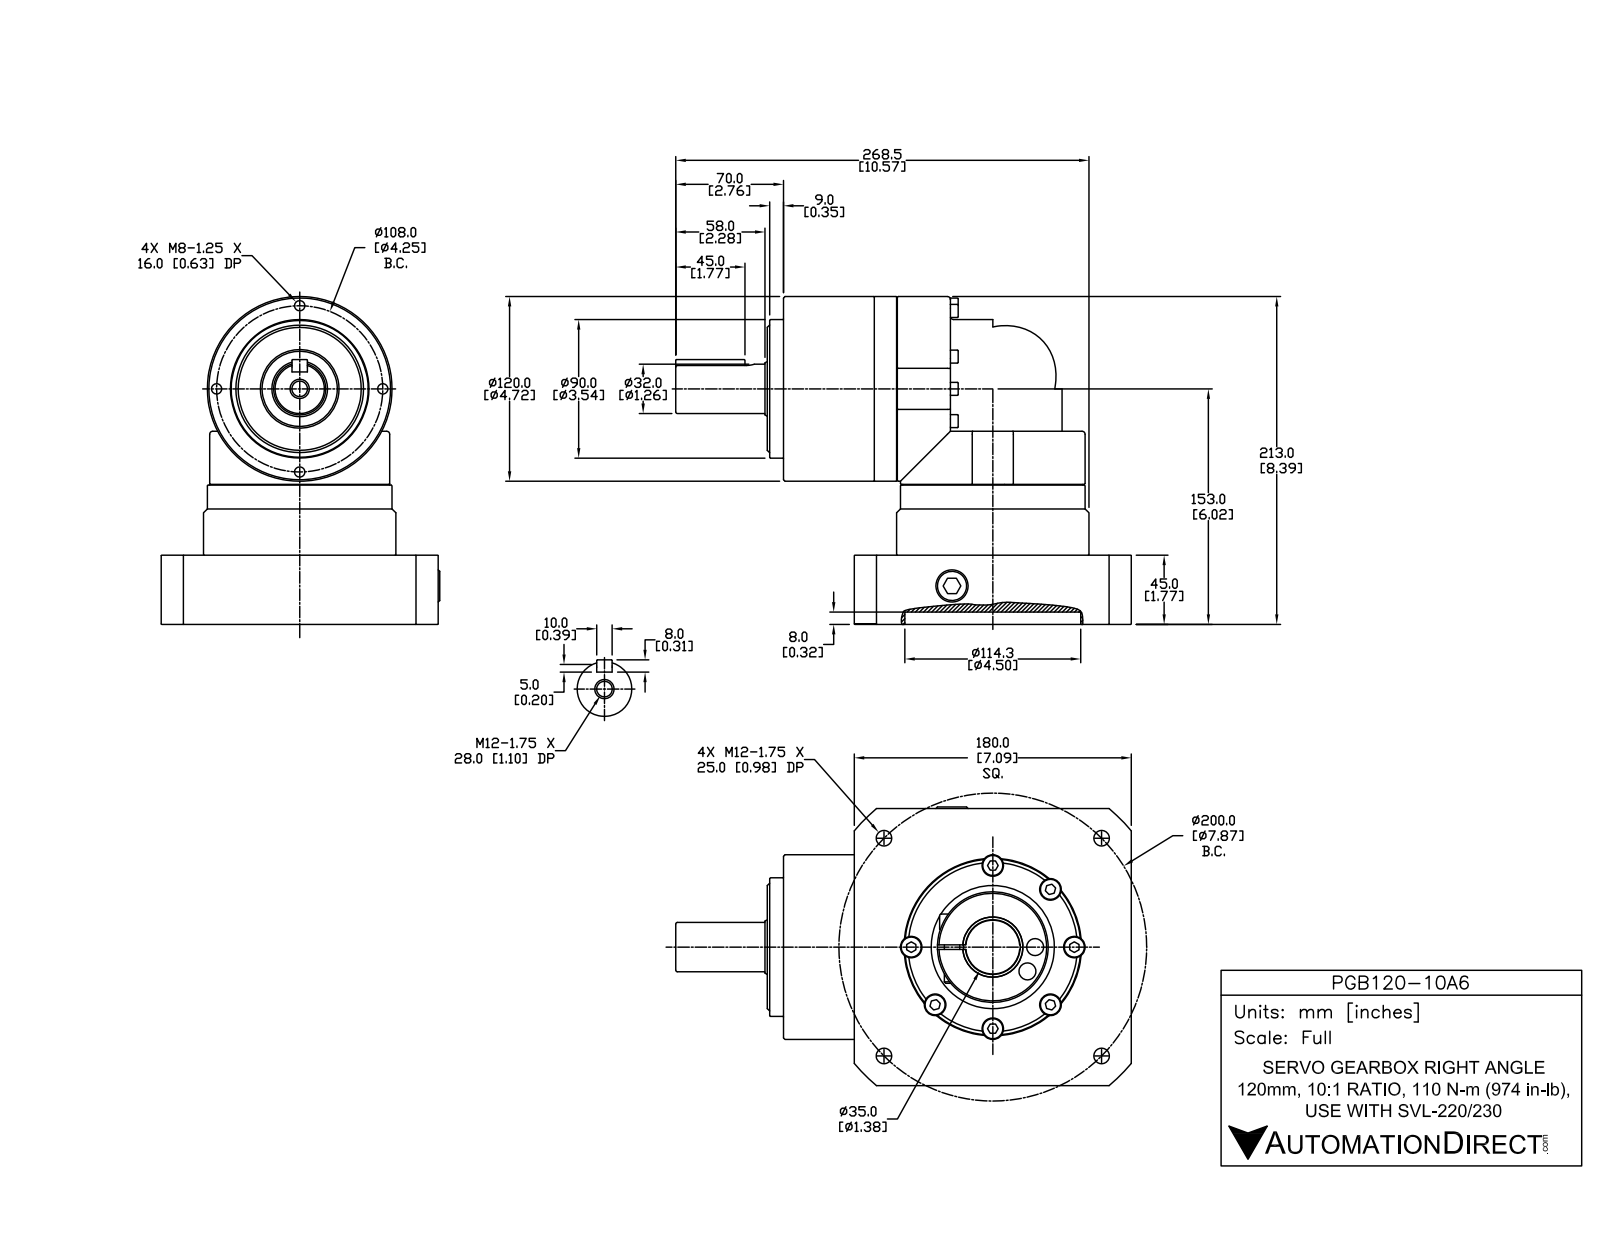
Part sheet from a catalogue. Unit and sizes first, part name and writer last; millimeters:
Units: millimetres
Overall size (bounding box): 296 × 213 × 181
Round holes (diameter × count): ⌀14 ×7, ⌀10.1 ×5, ⌀6.7 ×4, ⌀11 ×3, ⌀17.5 ×1, ⌀35 ×1, ⌀80 ×1
Round bosses / shafts (diameter × count): ⌀8.5 ×9, ⌀13 ×7, ⌀120 ×2, ⌀117 ×2, ⌀125 ×1, ⌀90 ×1, ⌀72 ×1, ⌀39 ×1
Partial cylindrical surfaces — rounded edges, fillets, slot ends (radius × count): R2 ×6, R2.5 ×2, R4.2 ×1, R5 ×1, R45 ×1, R55 ×1, R57.2 ×1, R117.5 ×1
Main face-to-face distances: 45, 180, 46, 9, 226, 36, 56.5, 236.5, 10.5, 148.5
Hole centre spacings: 72.9, 142.5, 53, 40.6, 97.9, 113.2, 54, 75
Volume: 3 608 000 mm³ · Surface area: 243 000 mm²
Bodies: 1 solid, 580 faces (245 planar, 150 cylindrical, 185 other)
Part name (STEP PRODUCT): PGB120-10A6
STEP written by: SolidWorks 2014 (AUTOMOTIVE_DESIGN)
